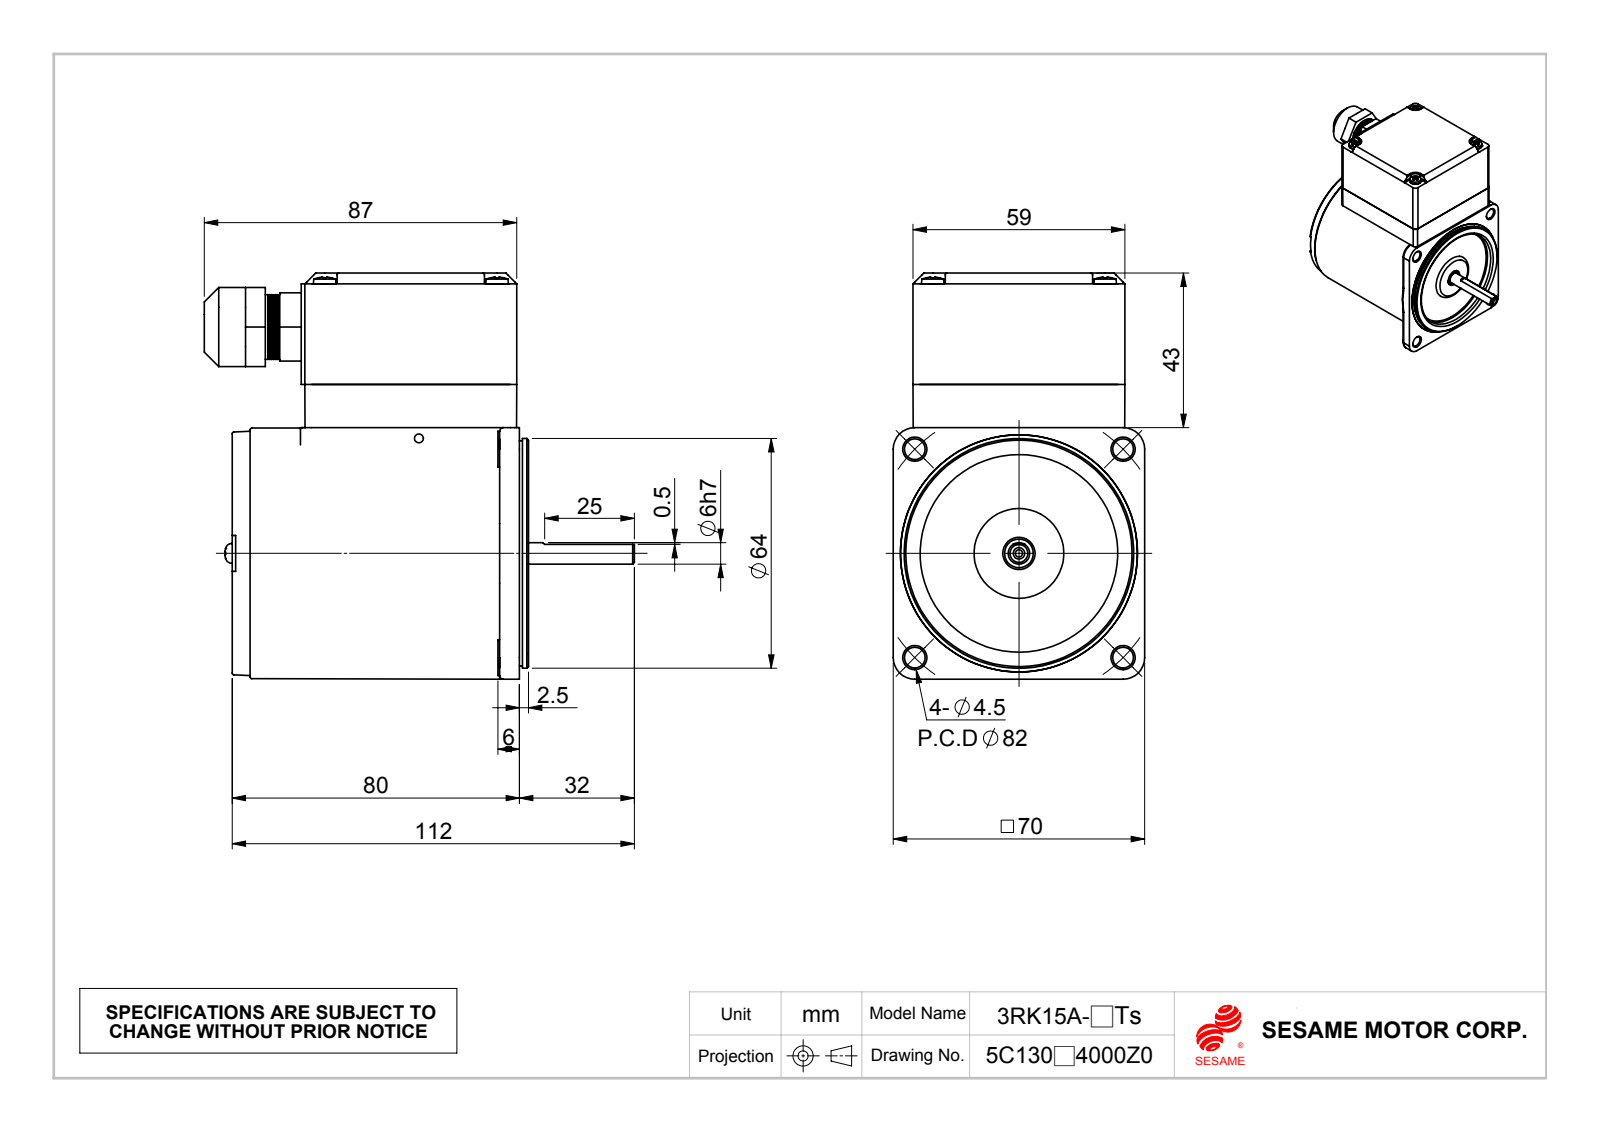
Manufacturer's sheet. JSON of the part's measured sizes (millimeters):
{"part_name": "成品180度; 15A_0.成品; 펥짰웰찿M3즤36x1t_Default; M315Ts-RK_3.鑽孔 (+2 more)", "step_written_by": "SolidWorks 2010 (CONFIG_CONTROL_DESIGN)", "units": "millimeters", "bodies": {"solids": 14, "faces": 2572, "planar": 250, "cylindrical": 891, "other": 1431}, "overall_size": [119.75, 113, 70], "volume_mm3": 227183, "surface_area_mm2": 92142, "round_holes": [[3.3, 4], [3.5, 4], [3.9, 4], [4.2, 4], [4.3, 4], [5.75, 4], [2.5, 3], [4, 2], [2, 1], [9, 1], [11, 1], [12, 1]], "round_bosses_or_shafts": [[3, 6], [10, 4], [6.3, 4], [5.5, 2], [63.93, 1], [62.73, 1], [57.42, 1], [57.2, 1]], "partial_cylinders_radius": [[0.5, 13], [2, 12], [0.3, 8], [1, 8], [5, 8], [4, 6], [1.5, 4], [2.75, 4]], "face_to_face_distances": [12, 0.75, 4, 1, 3, 1.5, 31, 43, 77.5, 74.5], "hole_center_spacings": [43.34, 14, 10.72, 19.8, 25.87, 27.01, 32.65, 41.01]}
